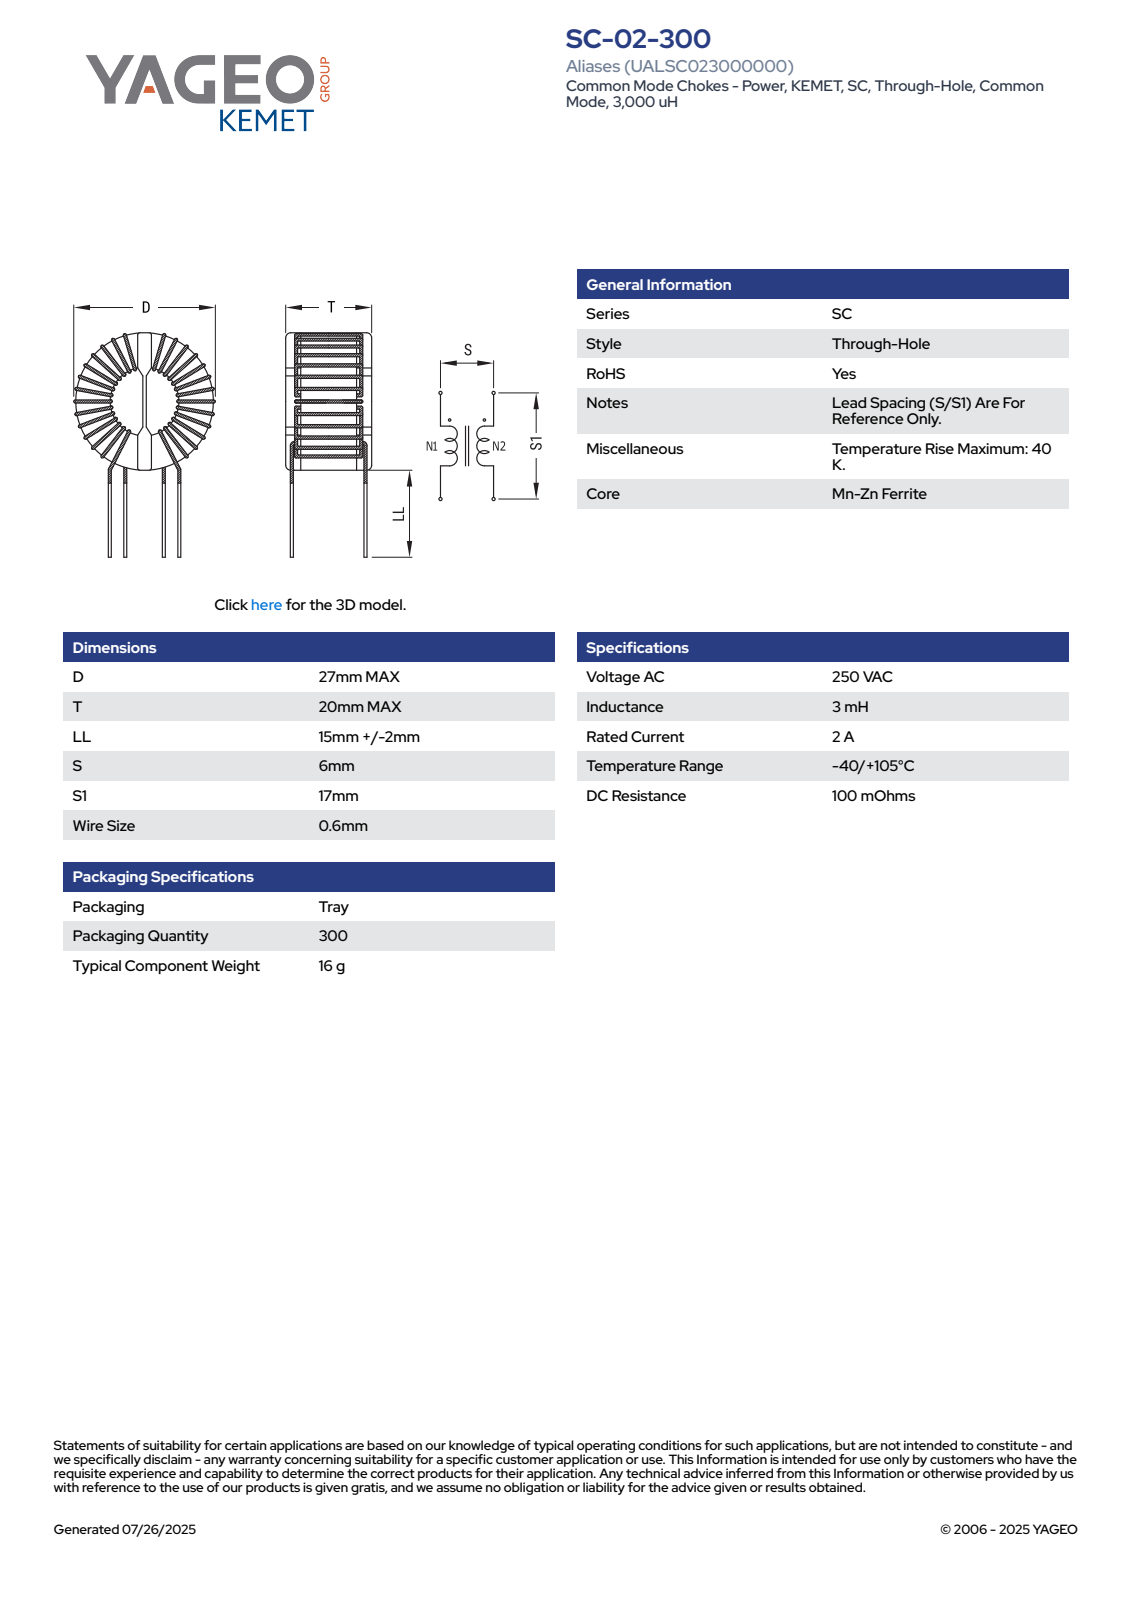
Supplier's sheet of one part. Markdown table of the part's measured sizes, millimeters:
| quantity | value |
| --- | --- |
| part name | SC-02-300 |
| STEP written by | SolidWorks 2018 (AUTOMOTIVE_DESIGN) |
| units | millimeters |
| bodies | 1 solid, 209 faces (62 planar, 79 cylindrical, 68 other) |
| overall size | 38.39 × 27 × 20 |
| volume | 7 651 mm³ |
| surface area | 4 216 mm² |
| round bosses / shafts (diameter × count) | 0.6 × 8 |
| partial cylindrical surfaces (radius × count) | 0.3 × 16, 0.2 × 4, 2.85 × 1, 4.15 × 1, 4.65 × 1, 4.75 × 1, 4.9 × 1, 9.25 × 1 |
| main face-to-face distances | 16.3, 1.2, 2, 3.2, 0.8, 1.85, 18.15, 3.48, 12.82, 3.92 |
